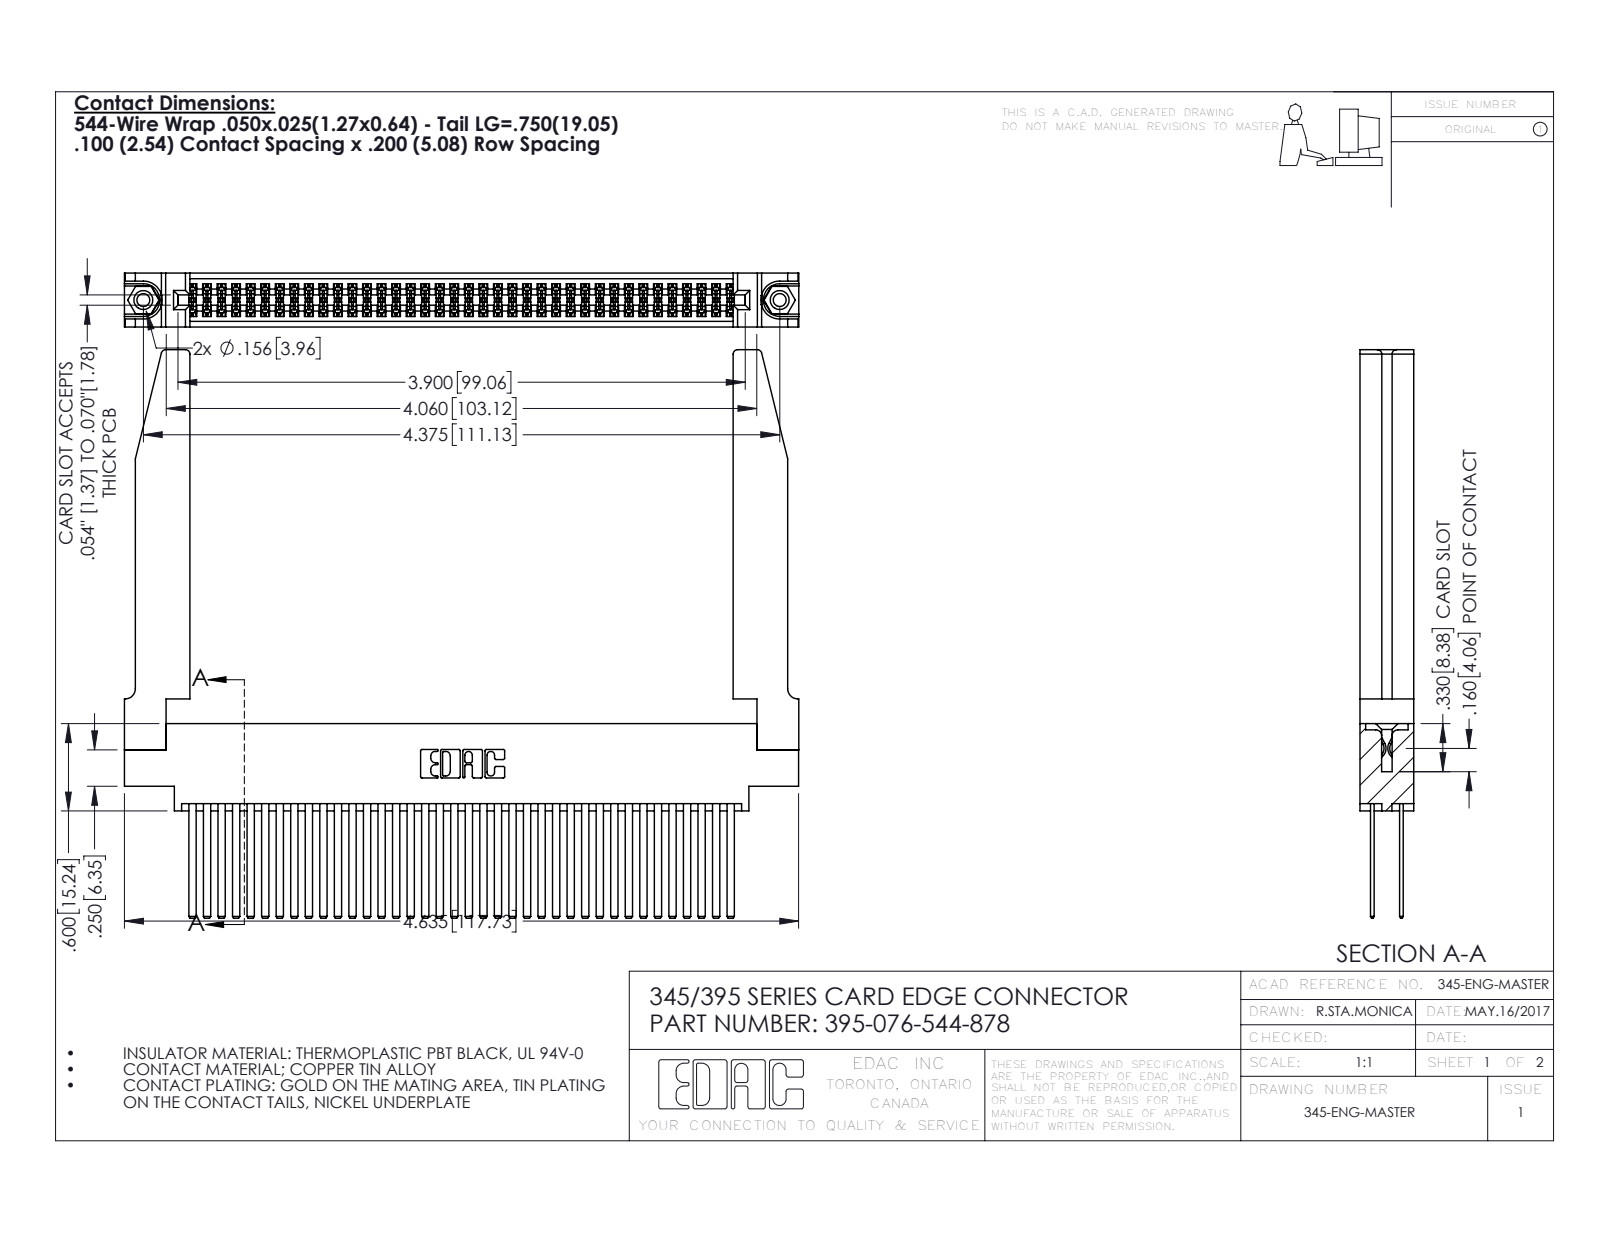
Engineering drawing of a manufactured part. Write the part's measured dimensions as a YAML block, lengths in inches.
part_name: "345 Part_0.170 Offset - 0.156 Dia-TH; 345-292-001_345-293-144; 345-250-001_345-250-001-102; 345-220-078_345-220-078 (+1 more)"
step_written_by: "SolidWorks 2016 (CONFIG_CONTROL_DESIGN)"
units: inches
bodies: {solids: 81, faces: 3708, planar: 2430, cylindrical: 1226, other: 52}
overall_size: [4.636, 3.907, 0.37]
volume: 1.228
surface_area: 43.85
round_holes:
  - {diameter: 0.089, count: 2}
  - {diameter: 0.125, count: 2}
  - {diameter: 0.156, count: 2}
  - {diameter: 0.064, count: 1}
round_bosses_or_shafts:
  - {diameter: 0.155, count: 2}
partial_cylinders:
  - {radius: 0.006, count: 114}
  - {radius: 0.01, count: 22}
  - {radius: 0.03, count: 8}
  - {radius: 0.007, count: 6}
  - {radius: 0.031, count: 6}
  - {radius: 0.026, count: 3}
  - {radius: 0.014, count: 2}
  - {radius: 0.019, count: 2}
face_to_face_distances: [0.072, 0.298, 0.098, 0.272, 0.025, 0.2, 0.37, 0.225, 0.175, 0.148]
hole_center_spacings: [0.27, 4.139, 4.375]
